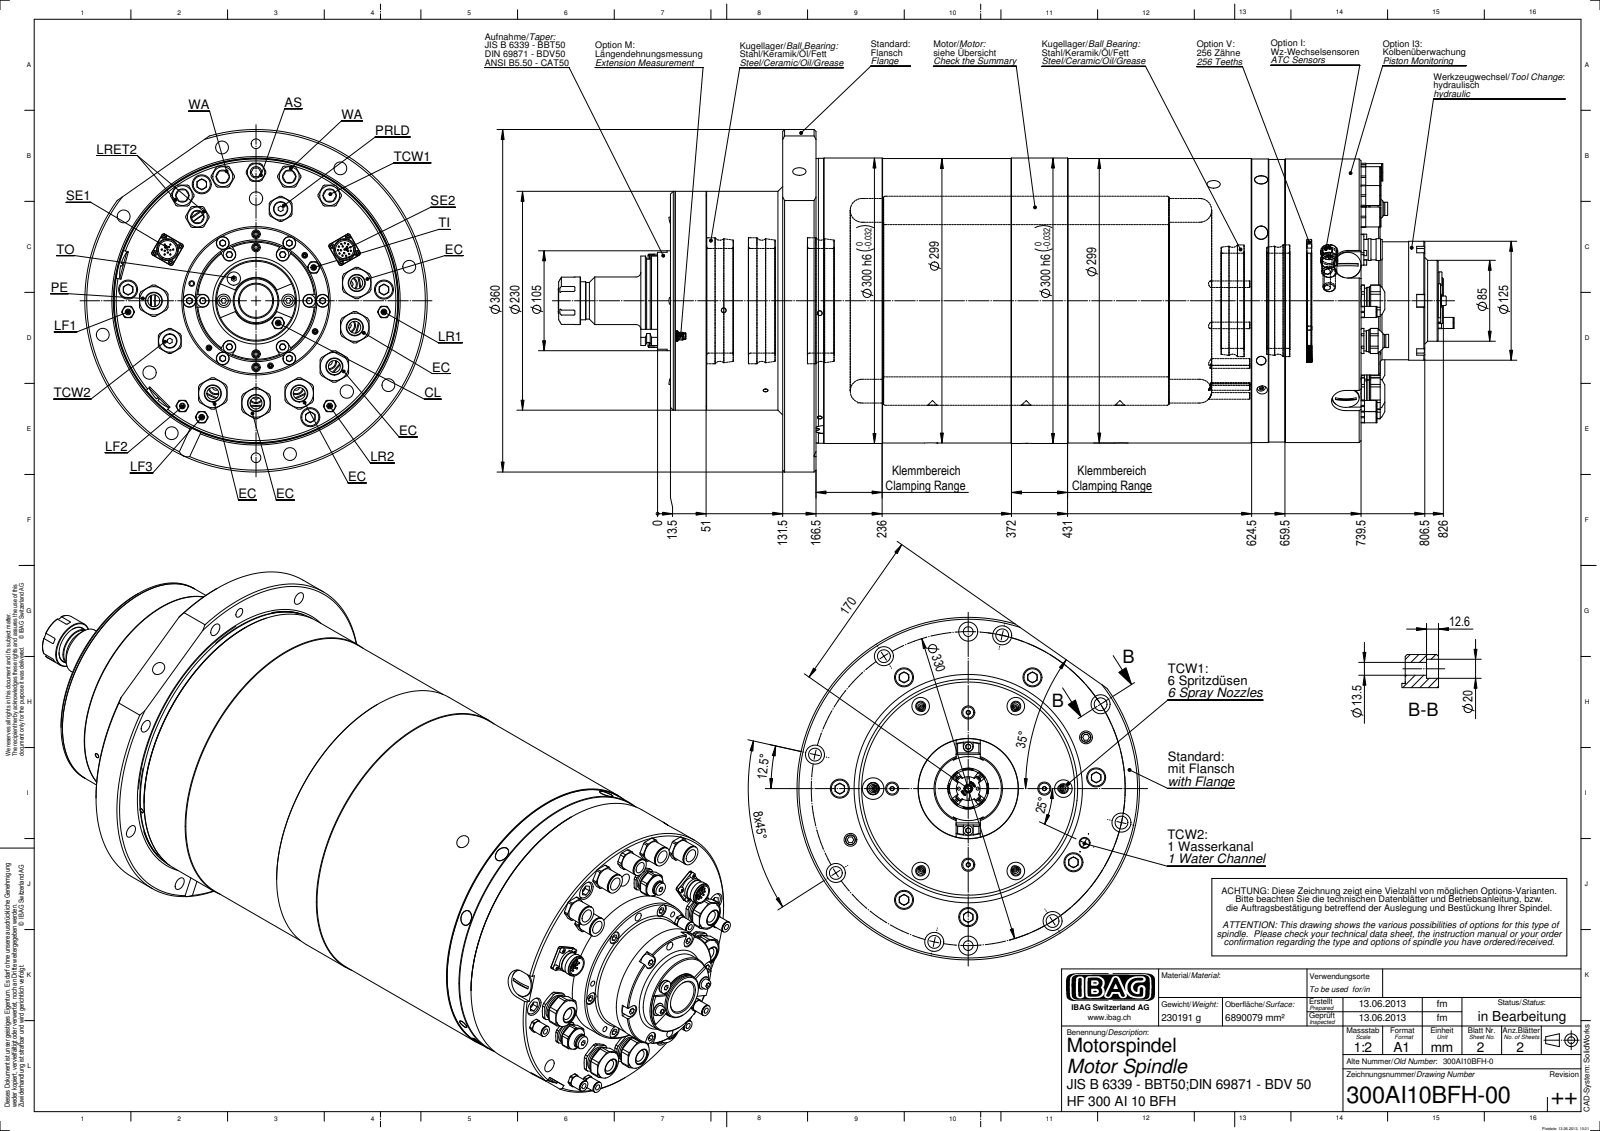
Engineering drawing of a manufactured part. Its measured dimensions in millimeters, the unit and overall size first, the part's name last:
Units: millimetres
Overall size (bounding box): 941.66 × 360 × 360
Round holes (diameter × count): ⌀20 ×20, ⌀13.5 ×16, ⌀14 ×13, ⌀6 ×12, ⌀5 ×7, ⌀12.5 ×7, ⌀17 ×7, ⌀10.5 ×5, ⌀12 ×5, ⌀9 ×4, ⌀30 ×3, ⌀10.2 ×2
Round bosses / shafts (diameter × count): ⌀1.5 ×28, ⌀5.5 ×8, ⌀29.8 ×7, ⌀28.23 ×7, ⌀26.42 ×7, ⌀13 ×7, ⌀11.7 ×7, ⌀7 ×6
Partial cylindrical surfaces — rounded edges, fillets, slot ends (radius × count): R1 ×12, R6.6 ×7, R16.5 ×7, R6.75 ×6, R12.25 ×5, R8.25 ×4, R13.2 ×2, R15 ×2
Main face-to-face distances: 608, 115, 493, 113, 606, 721, 5, 118, 611, 726
Hole centre spacings: 135, 100, 165, 304.88, 330, 44.23, 92.99, 126.28
Bodies: 0 solids, 1771 faces (695 planar, 774 cylindrical, 302 other)
Part name (STEP PRODUCT): 300AI10BFH-00
STEP written by: SolidWorks 2012 (CONFIG_CONTROL_DESIGN)
